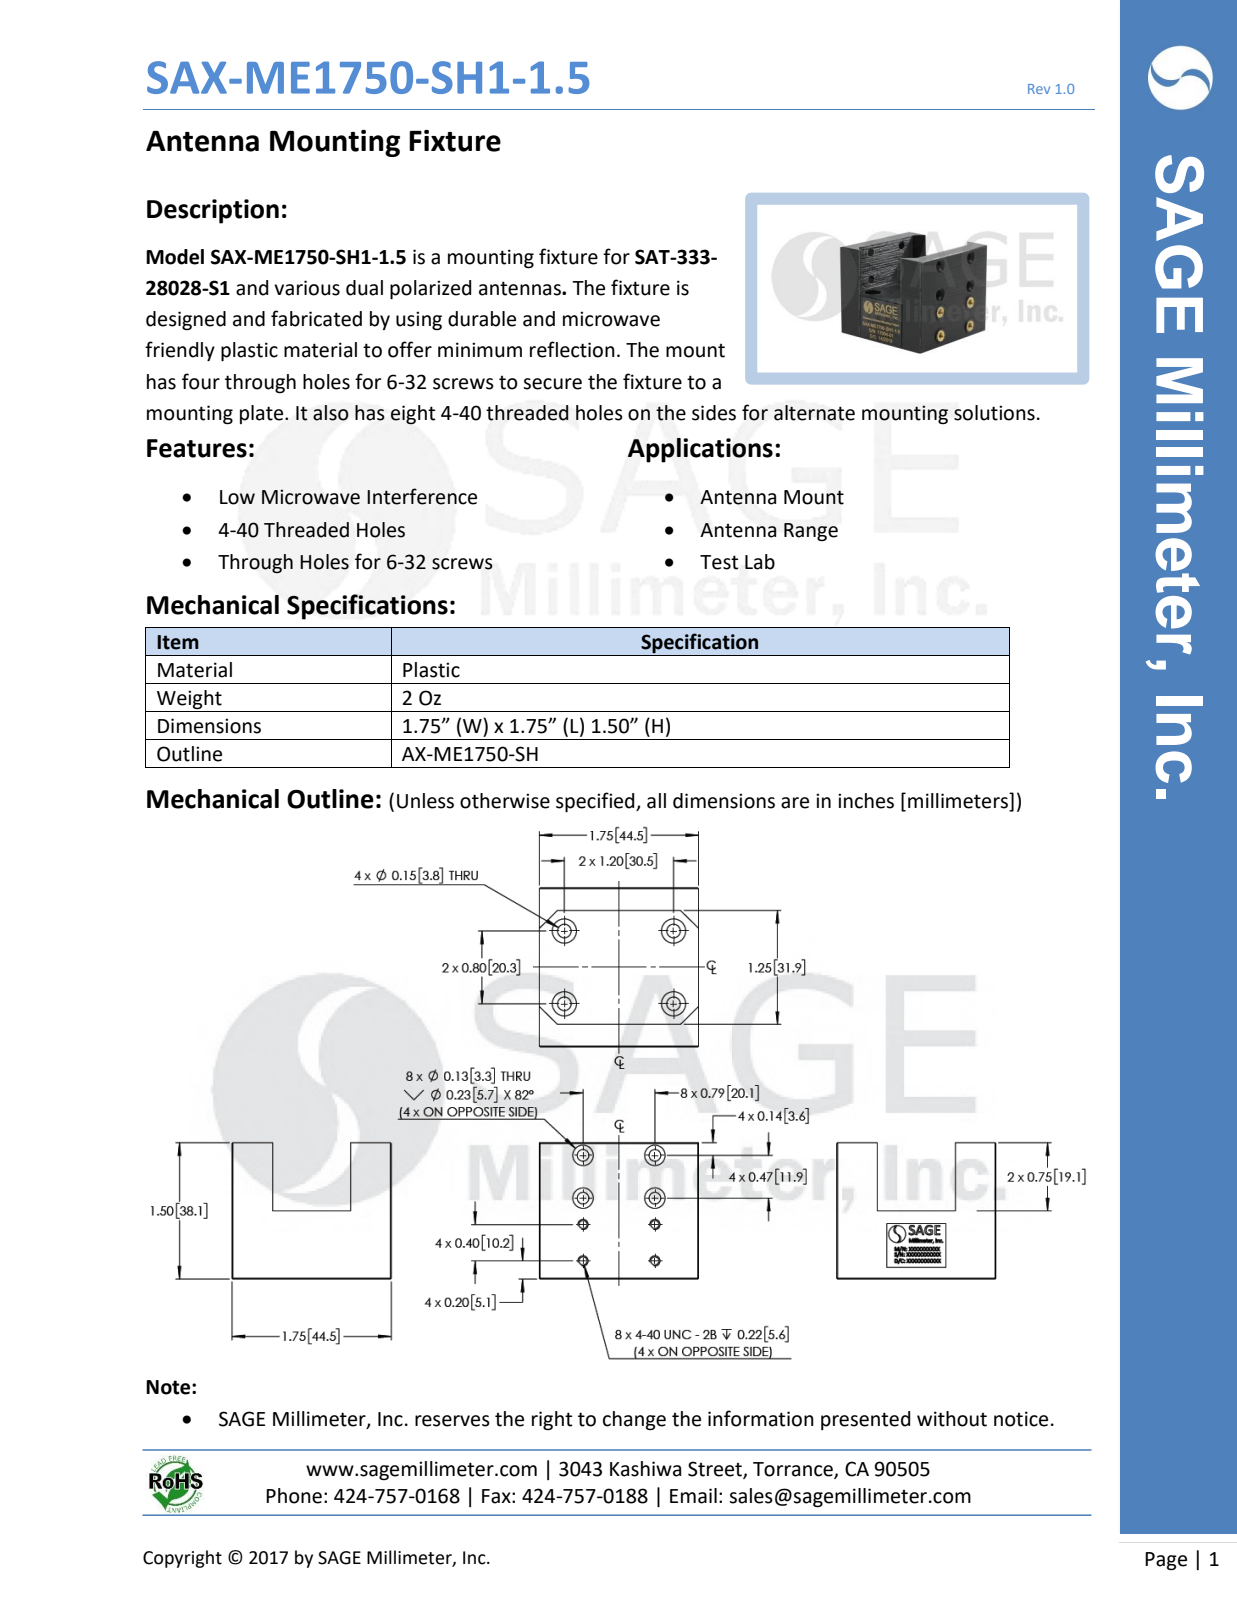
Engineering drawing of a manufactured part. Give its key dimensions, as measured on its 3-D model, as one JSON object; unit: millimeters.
{"part_name": "SAX-ME1750-SH1-1.5", "step_written_by": "SolidWorks 2021 (CONFIG_CONTROL_DESIGN)", "units": "millimeters", "bodies": {"solids": 1, "faces": 385, "planar": 59, "cylindrical": 238, "other": 88}, "overall_size": [44.5, 44.5, 38.1], "volume_mm3": 46560, "surface_area_mm2": 13920, "round_holes": [[2.8, 4], [3.2, 4], [3.3, 4], [3.9, 4], [6.8, 4], [3, 1], [3, 1], [3.1, 1], [3.7, 1], [3.7, 1], [3.8, 1], [3.8, 1]], "round_bosses_or_shafts": [[3.3, 4]], "face_to_face_distances": [19.1, 44.5, 6.1, 38.4, 44.5, 32.3, 38.1, 47.2, 6.4, 12.7], "hole_center_spacings": [20.1, 7.4, 10.2, 11.9, 17.5, 19.3, 20.3, 21.4]}
